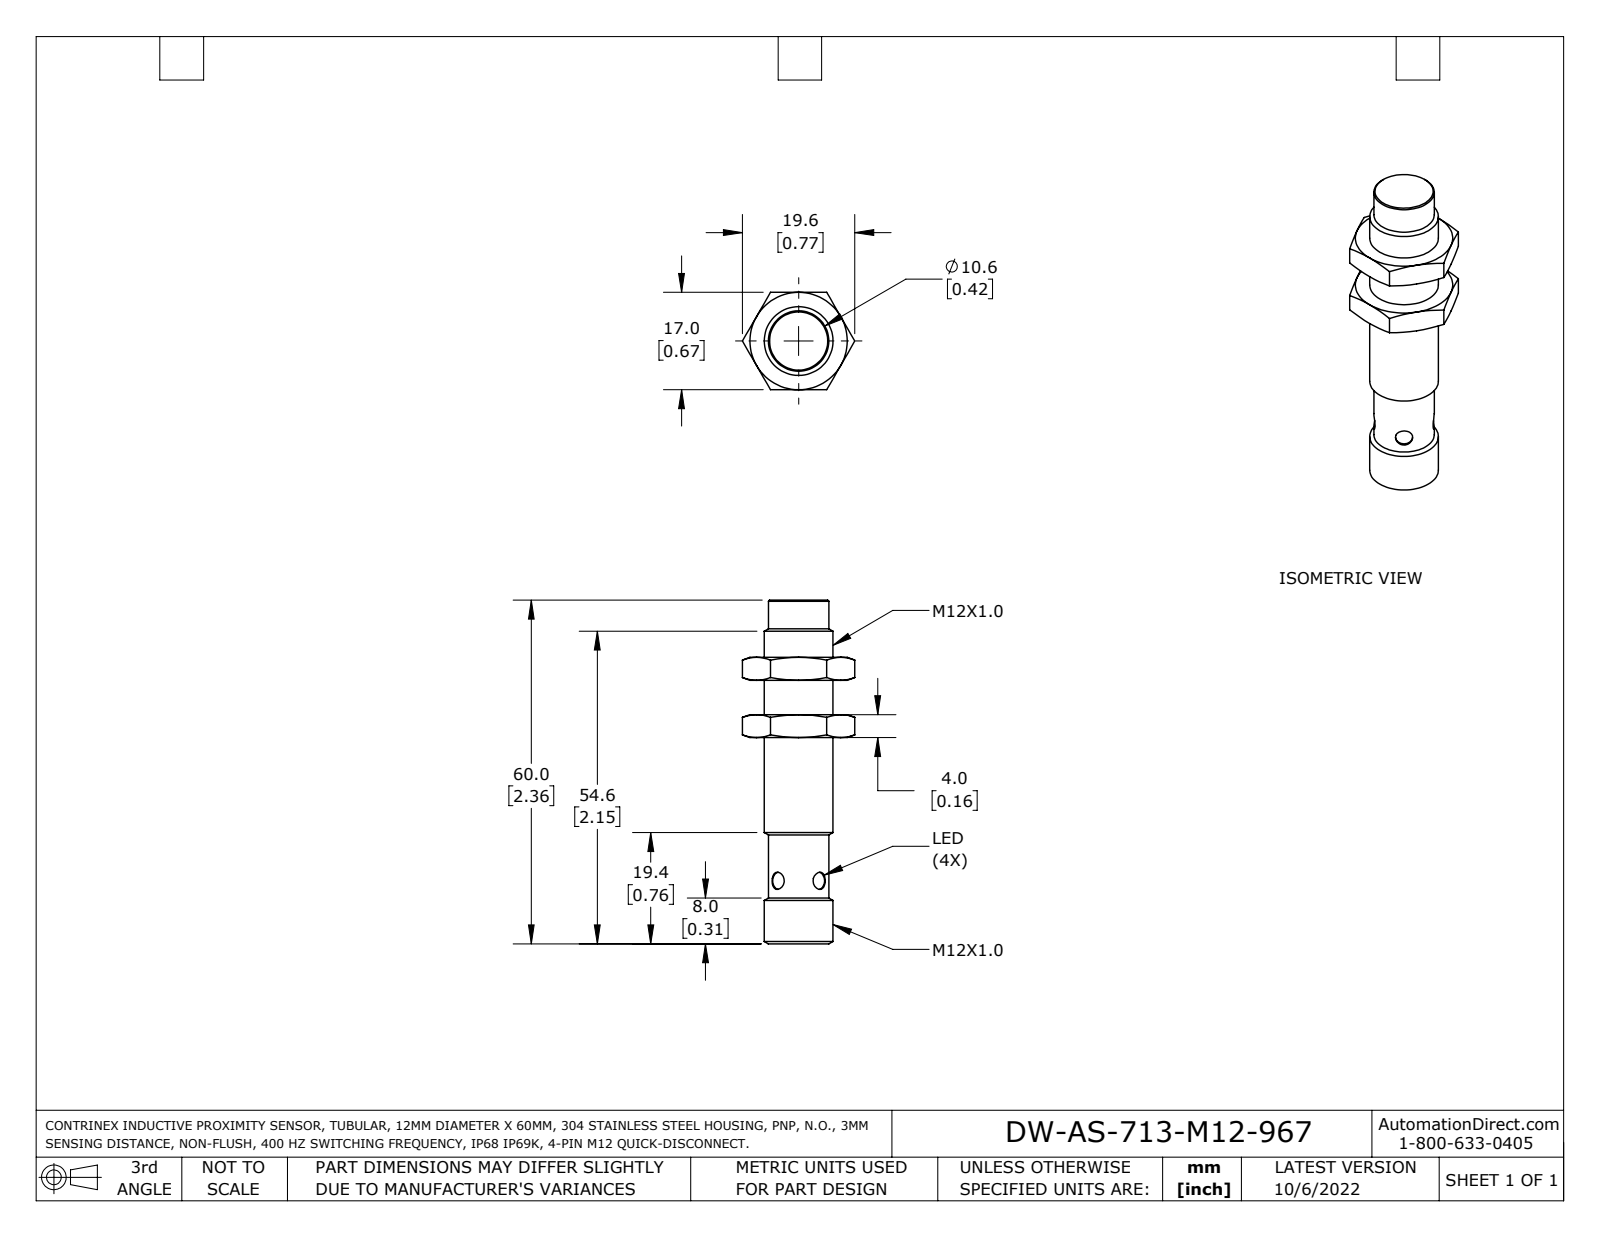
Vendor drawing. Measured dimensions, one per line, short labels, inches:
name: DW-AS-713-M12-967
written by: SolidWorks 2021 (AUTOMOTIVE_DESIGN)
unit: in
bodies: 1 solid, 77 faces (25 planar, 17 cylindrical, 35 other)
size: 2.362 × 0.773 × 0.669
volume: 0.425 in³; area: 5.326 in²
holes: 2× ⌀0.118, 1× ⌀0.335
bosses: 4× ⌀0.039, 1× ⌀0.472, 1× ⌀0.415
rounds: 2× R0.022
face distances: 0.394, 0.157, 0.669, 0.551, 0.236, 0.787, 0.945, 2.02, 1.626, 1.469
